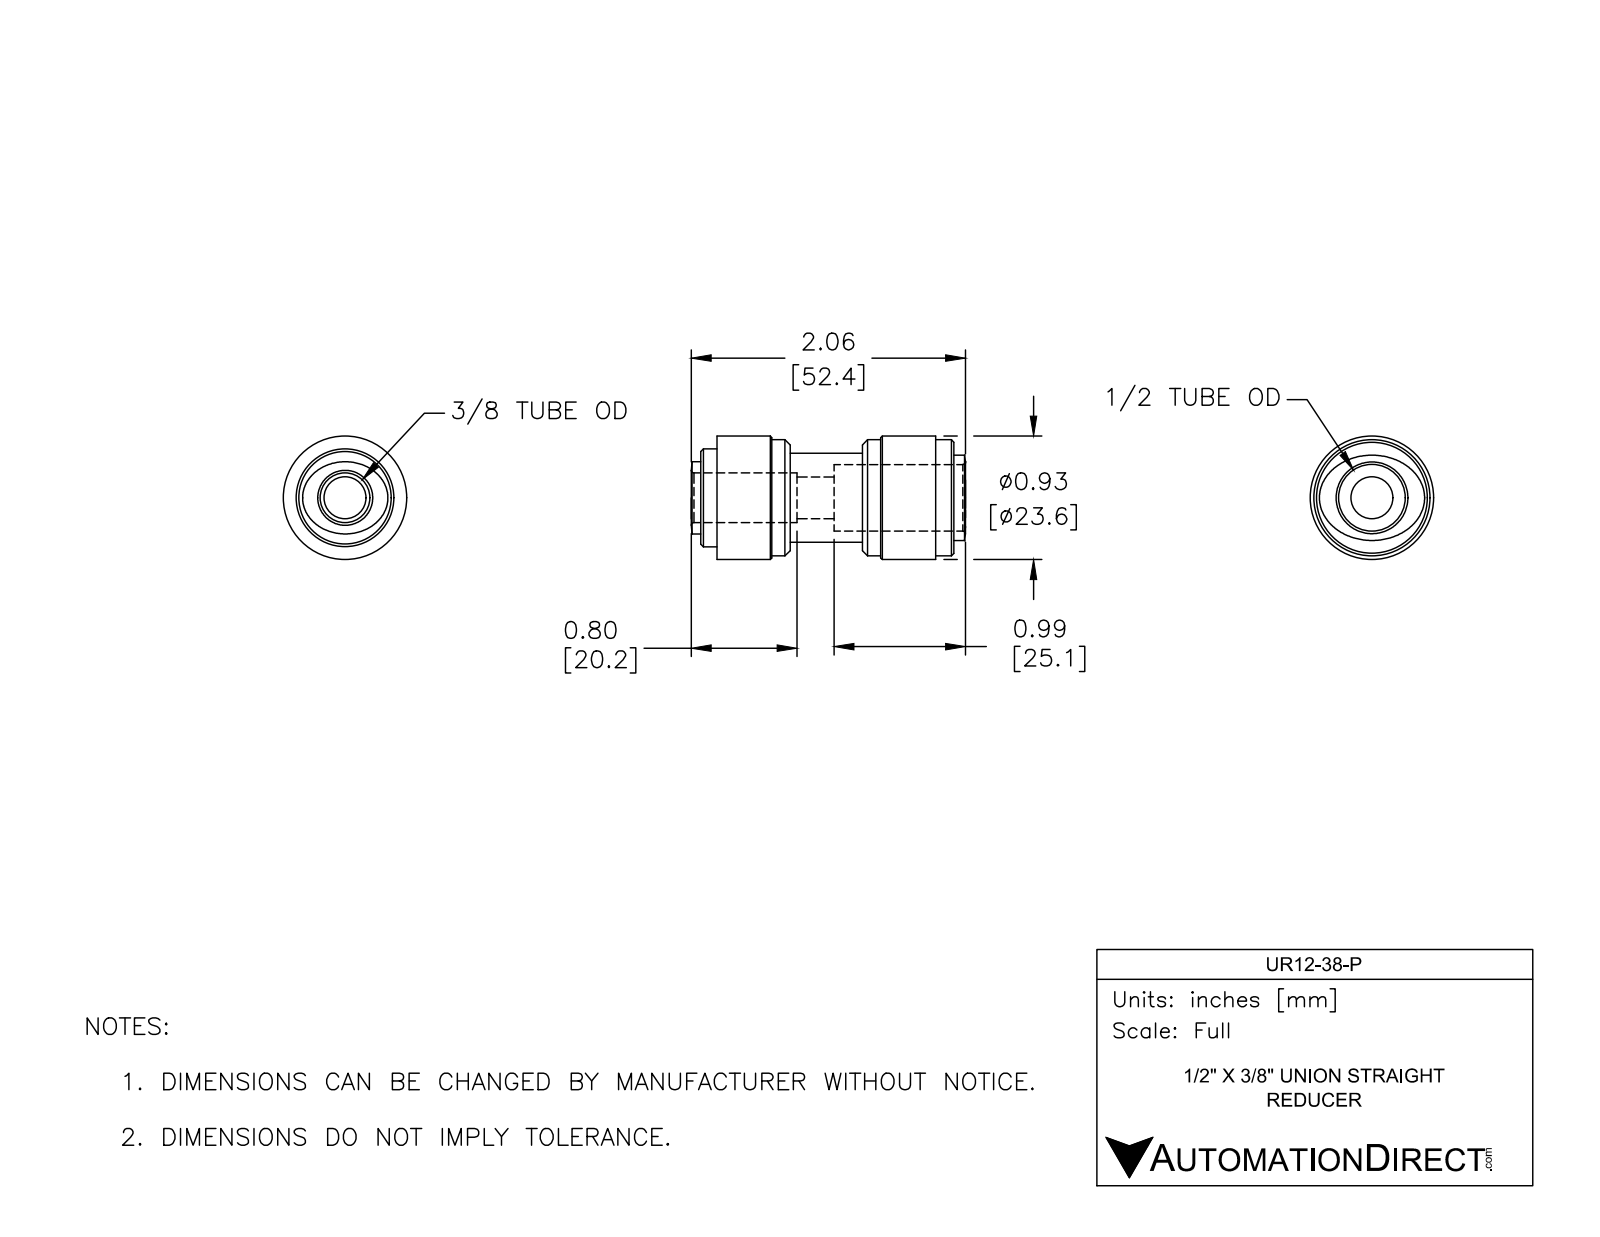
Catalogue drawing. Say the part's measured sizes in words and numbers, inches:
The part is named "UR12-38-P". Its 3-D file was written by "SolidWorks 2017 (AUTOMOTIVE_DESIGN)". It is 1 solid with 54 faces: 10 planar, 20 cylindrical and 24 other. Overall it measures 2.063 by 0.929 by 0.929 inches. Its volume is 0.795 cubic inches and its surface area 9.636 square inches. Round holes: 1 of diameter 0.315, 1 of diameter 0.374, 1 of diameter 0.5. Round bosses or shafts: 1 of diameter 0.929, 1 of diameter 0.874, 1 of diameter 0.736, 1 of diameter 0.669. The main face-to-face distances are 0.551, 1.232, 1.094, 0.138, 1.783, 0.689, 0.543, 0.902, 0.213, 0.331.
